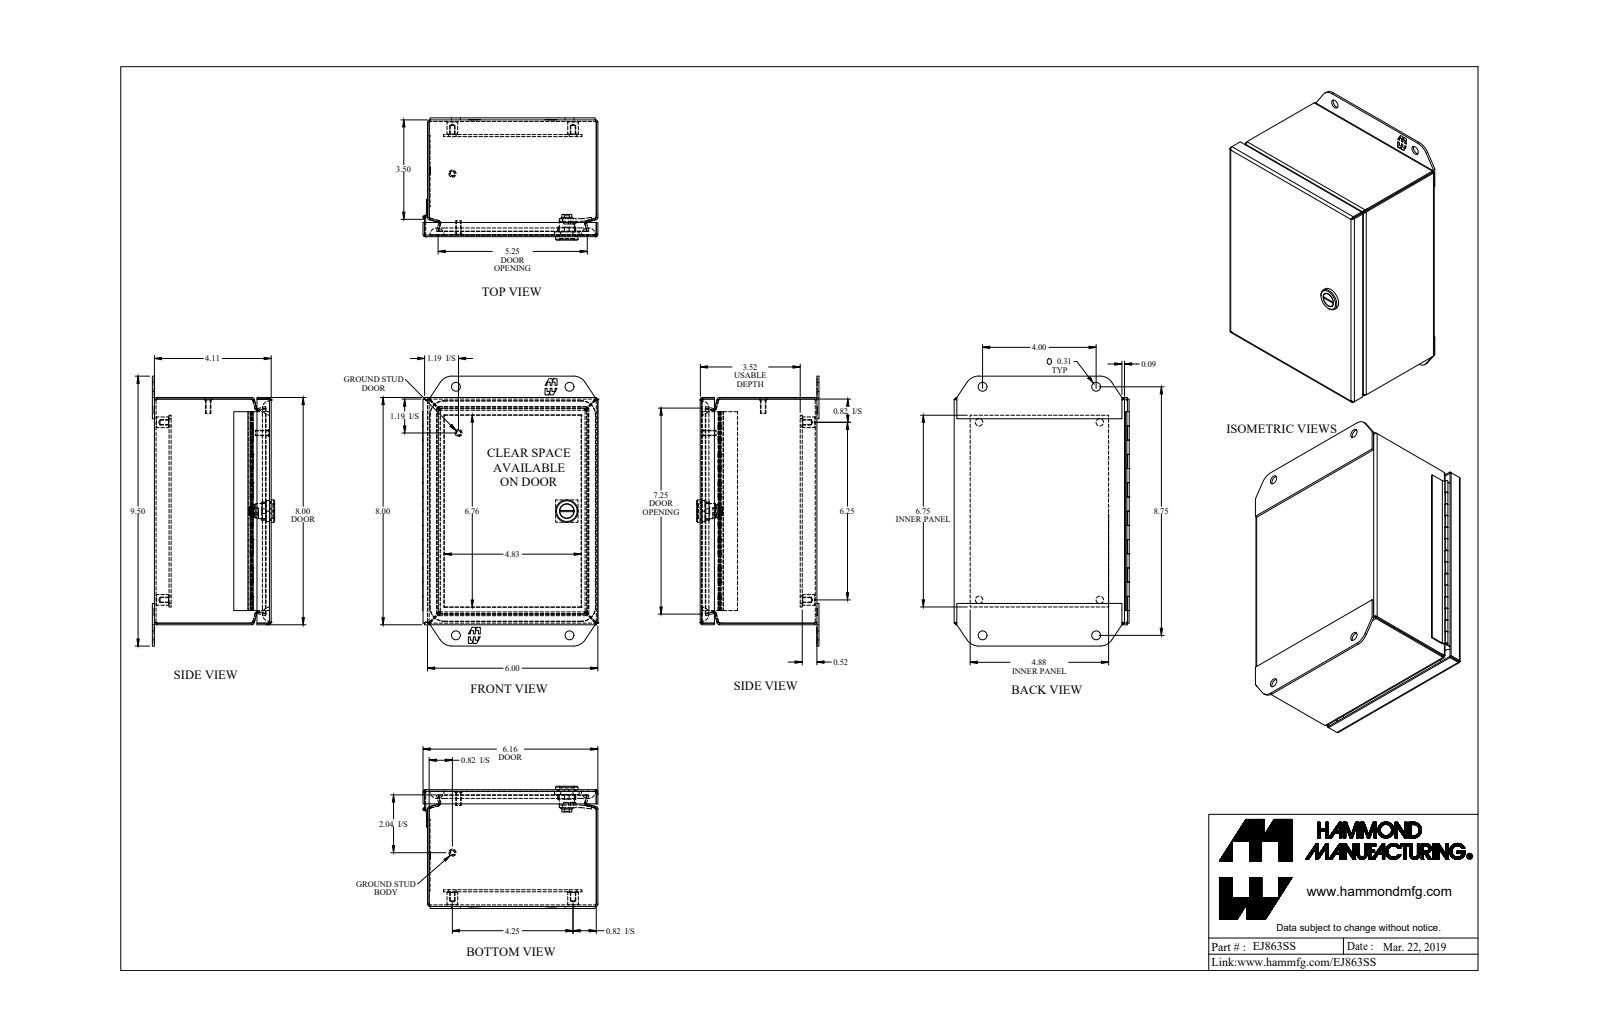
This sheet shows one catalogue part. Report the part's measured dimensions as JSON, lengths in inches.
{"part_name": "EJ863SS_Default", "step_written_by": "SolidWorks 2019 (CONFIG_CONTROL_DESIGN)", "units": "inches", "bodies": {"solids": 16, "faces": 656, "planar": 370, "cylindrical": 190, "other": 96}, "overall_size": [9.5, 6.165, 4.305], "volume_in3": 19.35, "surface_area_in2": 636.1, "round_holes": [[0.156, 4], [0.265, 4], [0.313, 4], [0.05, 1], [0.516, 1]], "round_bosses_or_shafts": [[0.375, 4], [0.25, 2], [0.19, 2], [0.788, 1], [0.535, 1], [0.496, 1], [0.435, 1], [0.1, 1]], "partial_cylinders_radius": [[0.029, 16], [0.086, 16], [0.281, 12], [0.25, 4], [0.499, 4], [0.5, 4], [0.06, 2], [0.03, 1]], "face_to_face_distances": [0.057, 4.054, 5.943, 0.072, 0.589, 4.111, 3.997, 7.943, 3.594, 3.537], "hole_center_spacings": [1.256, 4.31, 7.502, 8.56, 3.133, 4, 4.25, 4.376]}
